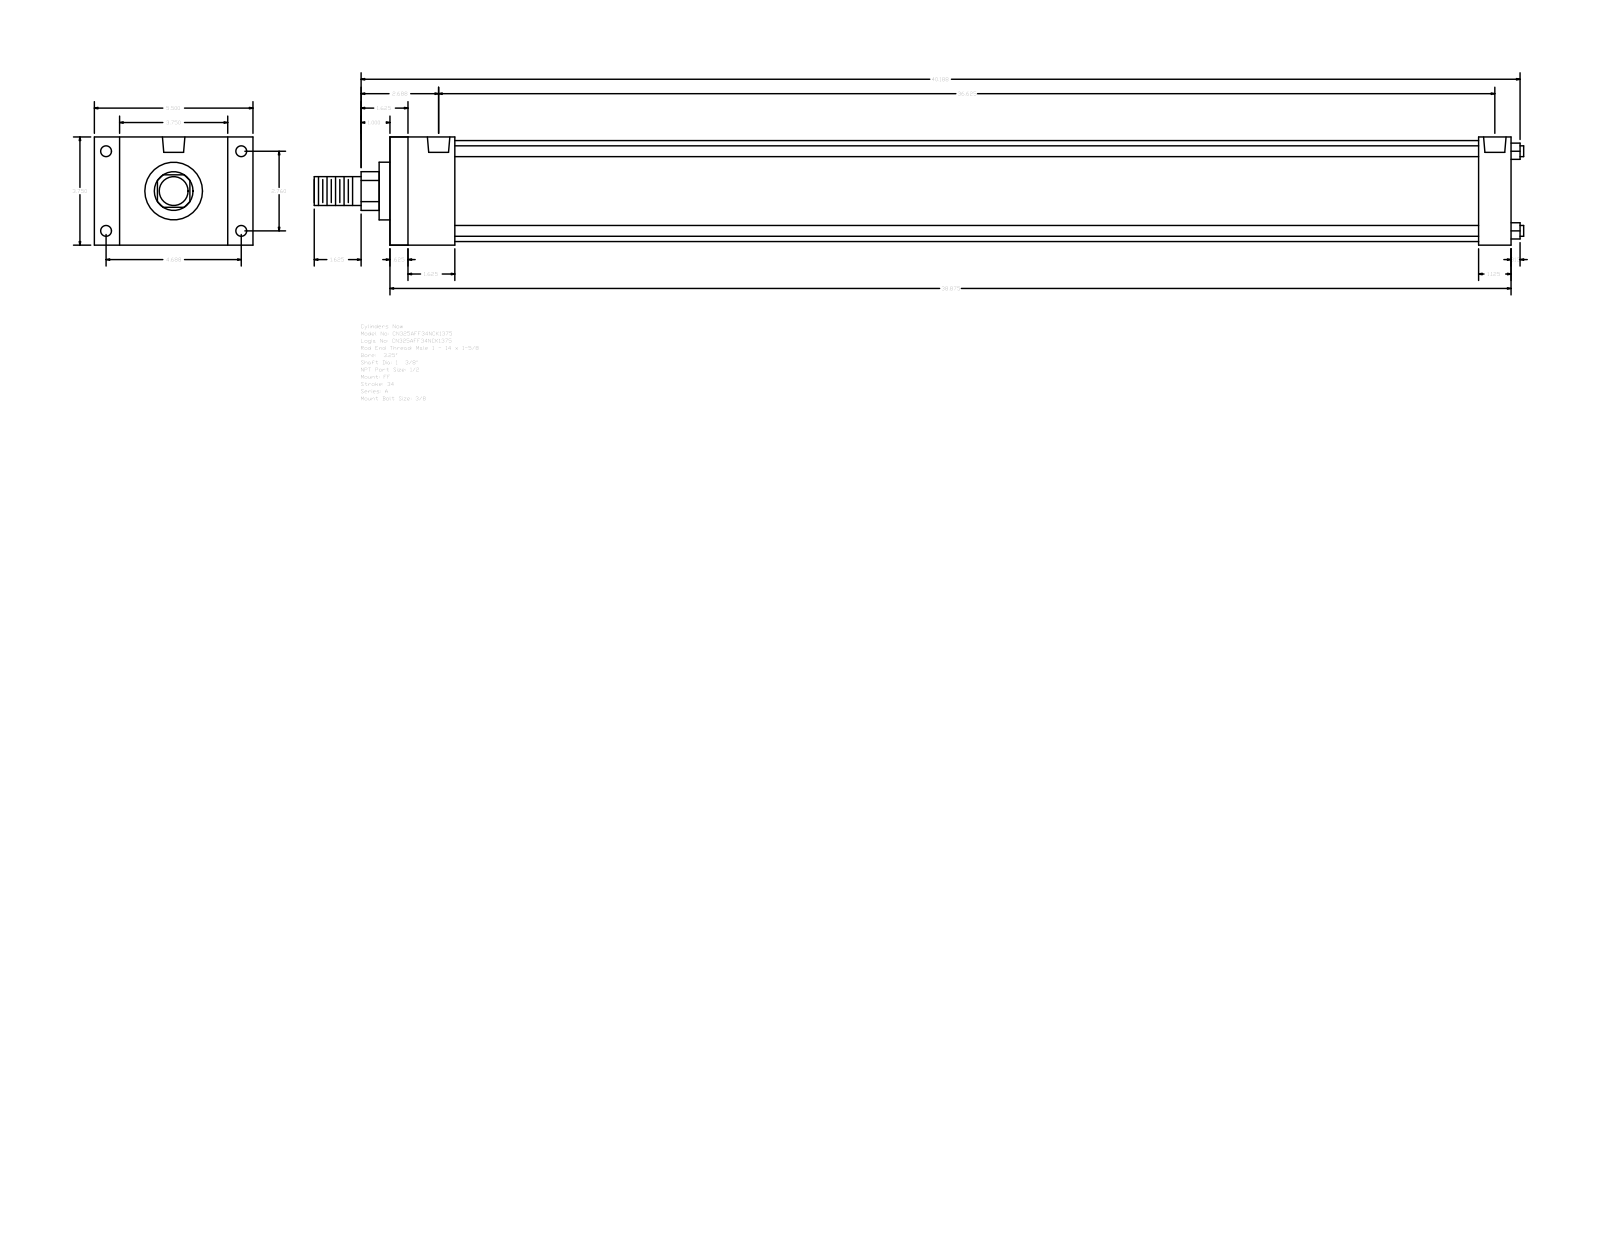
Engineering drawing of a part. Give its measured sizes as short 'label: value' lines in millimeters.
name: A_FF__0325_1.375
written by: GSSL Pune (CONFIG_CONTROL_DESIGN)
unit: mm
bodies: 0 solids, 92 faces (64 planar, 28 cylindrical, 0 other)
size: 1065.21 × 139.7 × 95.25
holes: 4× ⌀8.73, 4× ⌀9.53, 2× ⌀19.77
bosses: 4× ⌀9.53, 1× ⌀88.9, 1× ⌀50.8, 1× ⌀34.92, 1× ⌀25.4
rounds: 1× R17.06
face distances: 95.24, 987.43, 15.87, 971.56, 57.15, 28.58, 22.23, 117.47, 958.85, 41.28
hole spacings: 3.18, 70.1, 119.06, 138.16, 923.92, 927.1, 930.28
